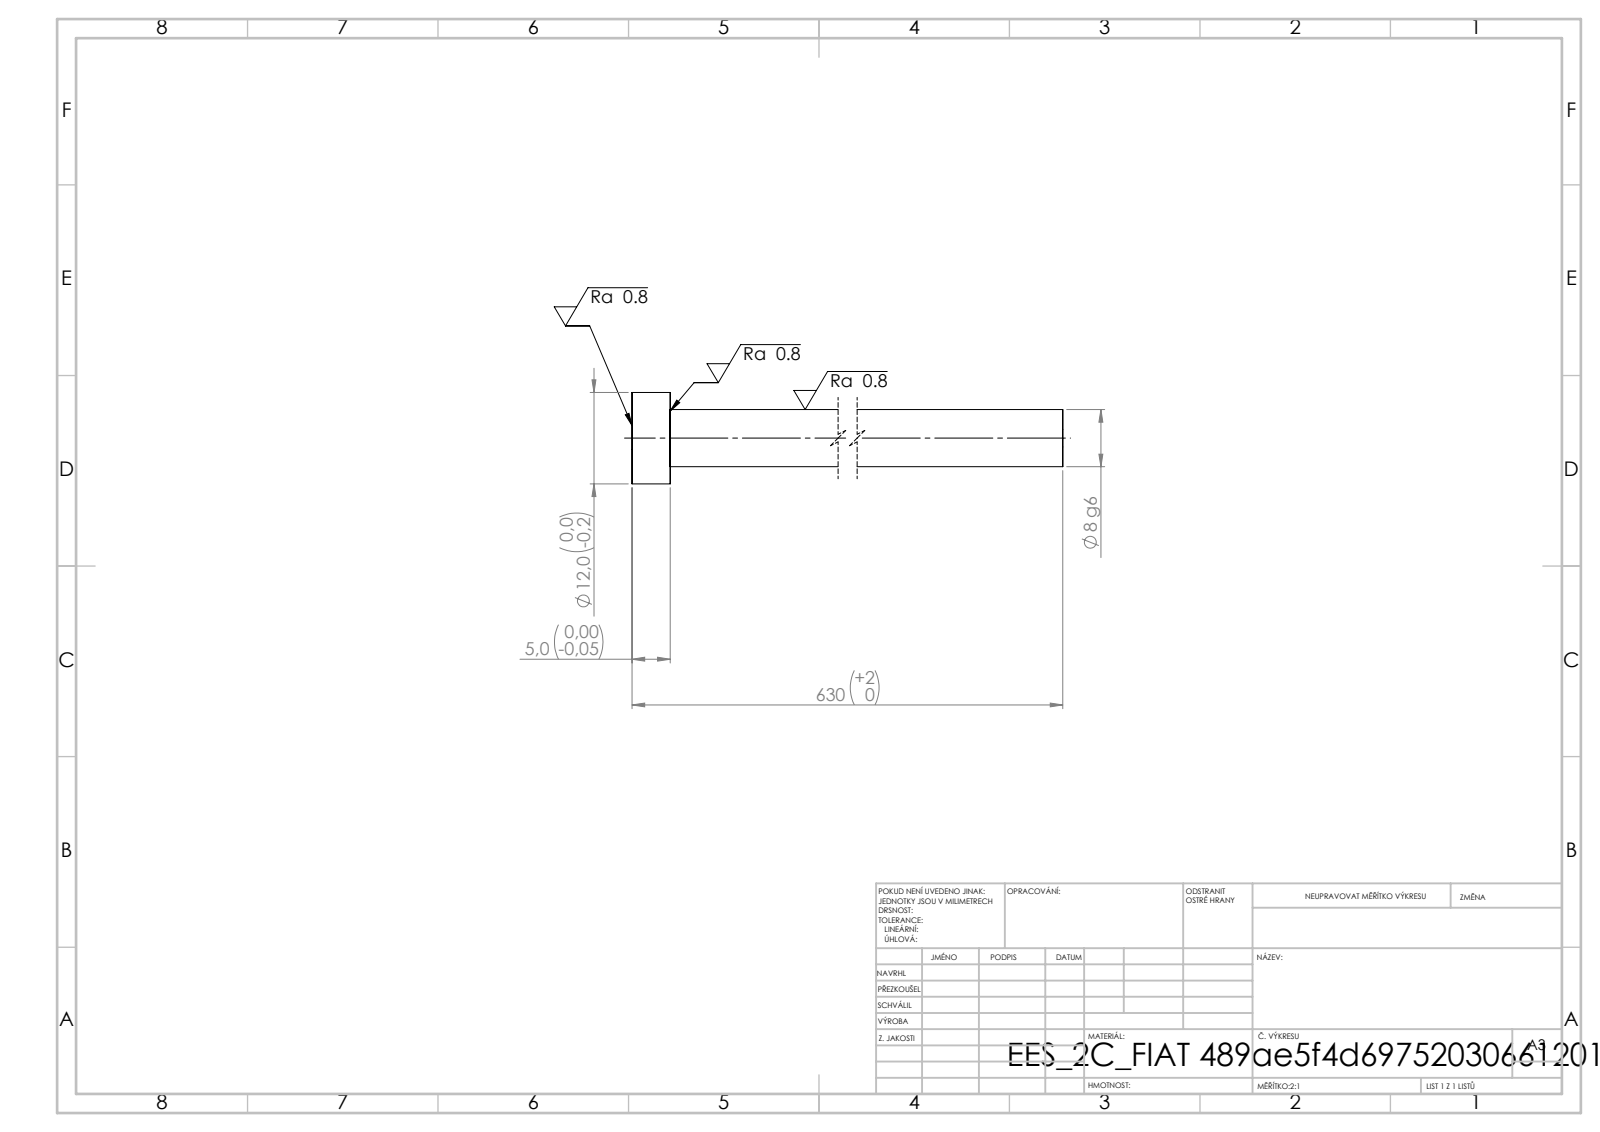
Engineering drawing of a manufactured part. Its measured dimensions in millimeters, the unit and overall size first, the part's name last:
Units: millimetres
Overall size (bounding box): 630 × 12 × 12
Round bosses / shafts (diameter × count): ⌀12 ×1, ⌀7.5 ×1
Main face-to-face distances: 5, 630, 625
Volume: 28 177 mm³ · Surface area: 15 141 mm²
Bodies: 1 solid, 7 faces (3 planar, 4 cylindrical, 0 other)
STEP written by: SolidWorks 2019 (CONFIG_CONTROL_DESIGN)
